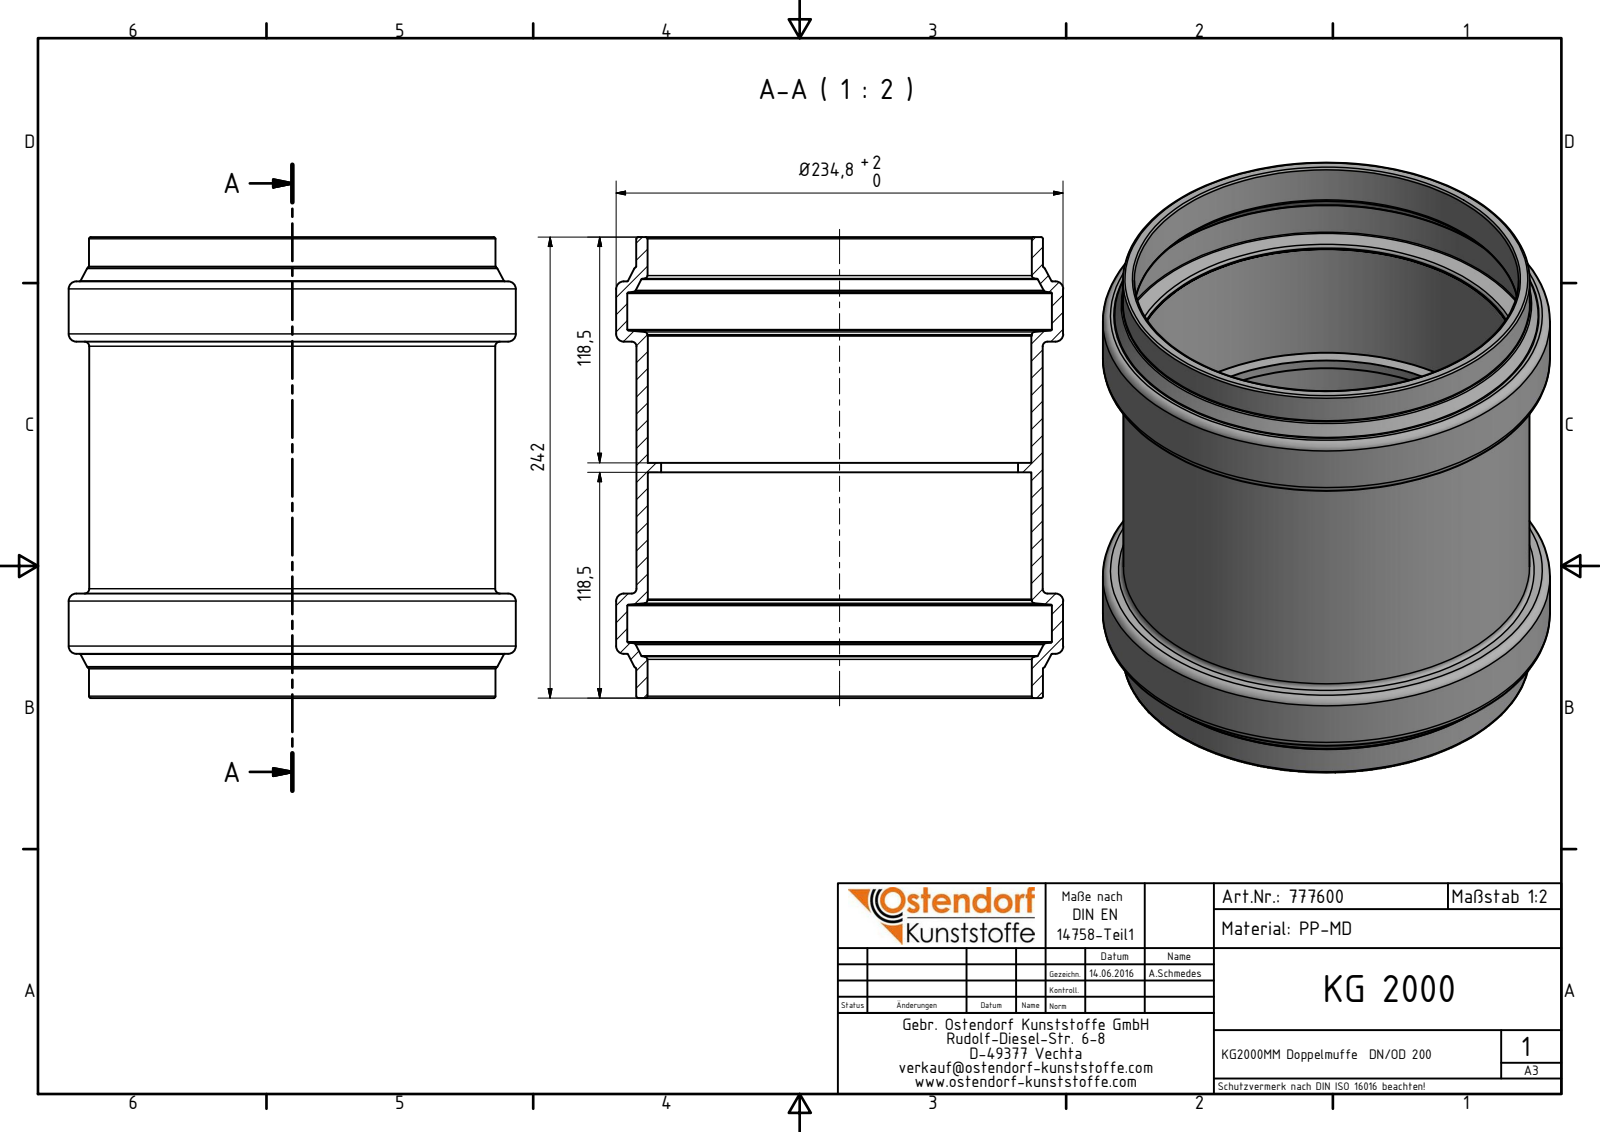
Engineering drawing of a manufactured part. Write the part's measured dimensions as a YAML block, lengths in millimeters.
part_name: "777600 KG2000MM Doppelmuffe DN_OD 200"
step_written_by: "Autodesk Inventor 2016 (AUTOMOTIVE_DESIGN)"
units: millimeters
bodies: {solids: 1, faces: 62, planar: 10, cylindrical: 14, other: 38}
overall_size: [242, 234.8, 234.8]
volume: 1106000
surface_area: 377845
round_holes:
  - {diameter: 187.5, count: 1}
  - {diameter: 201.5, count: 1}
  - {diameter: 201.8, count: 1}
  - {diameter: 223, count: 1}
round_bosses_or_shafts:
  - {diameter: 234.8, count: 1}
  - {diameter: 213.6, count: 1}
  - {diameter: 213.3, count: 1}
face_to_face_distances: [63.6, 68.6, 54.9, 118.5, 123.5, 187.1, 5, 132.2, 242, 23.3]
